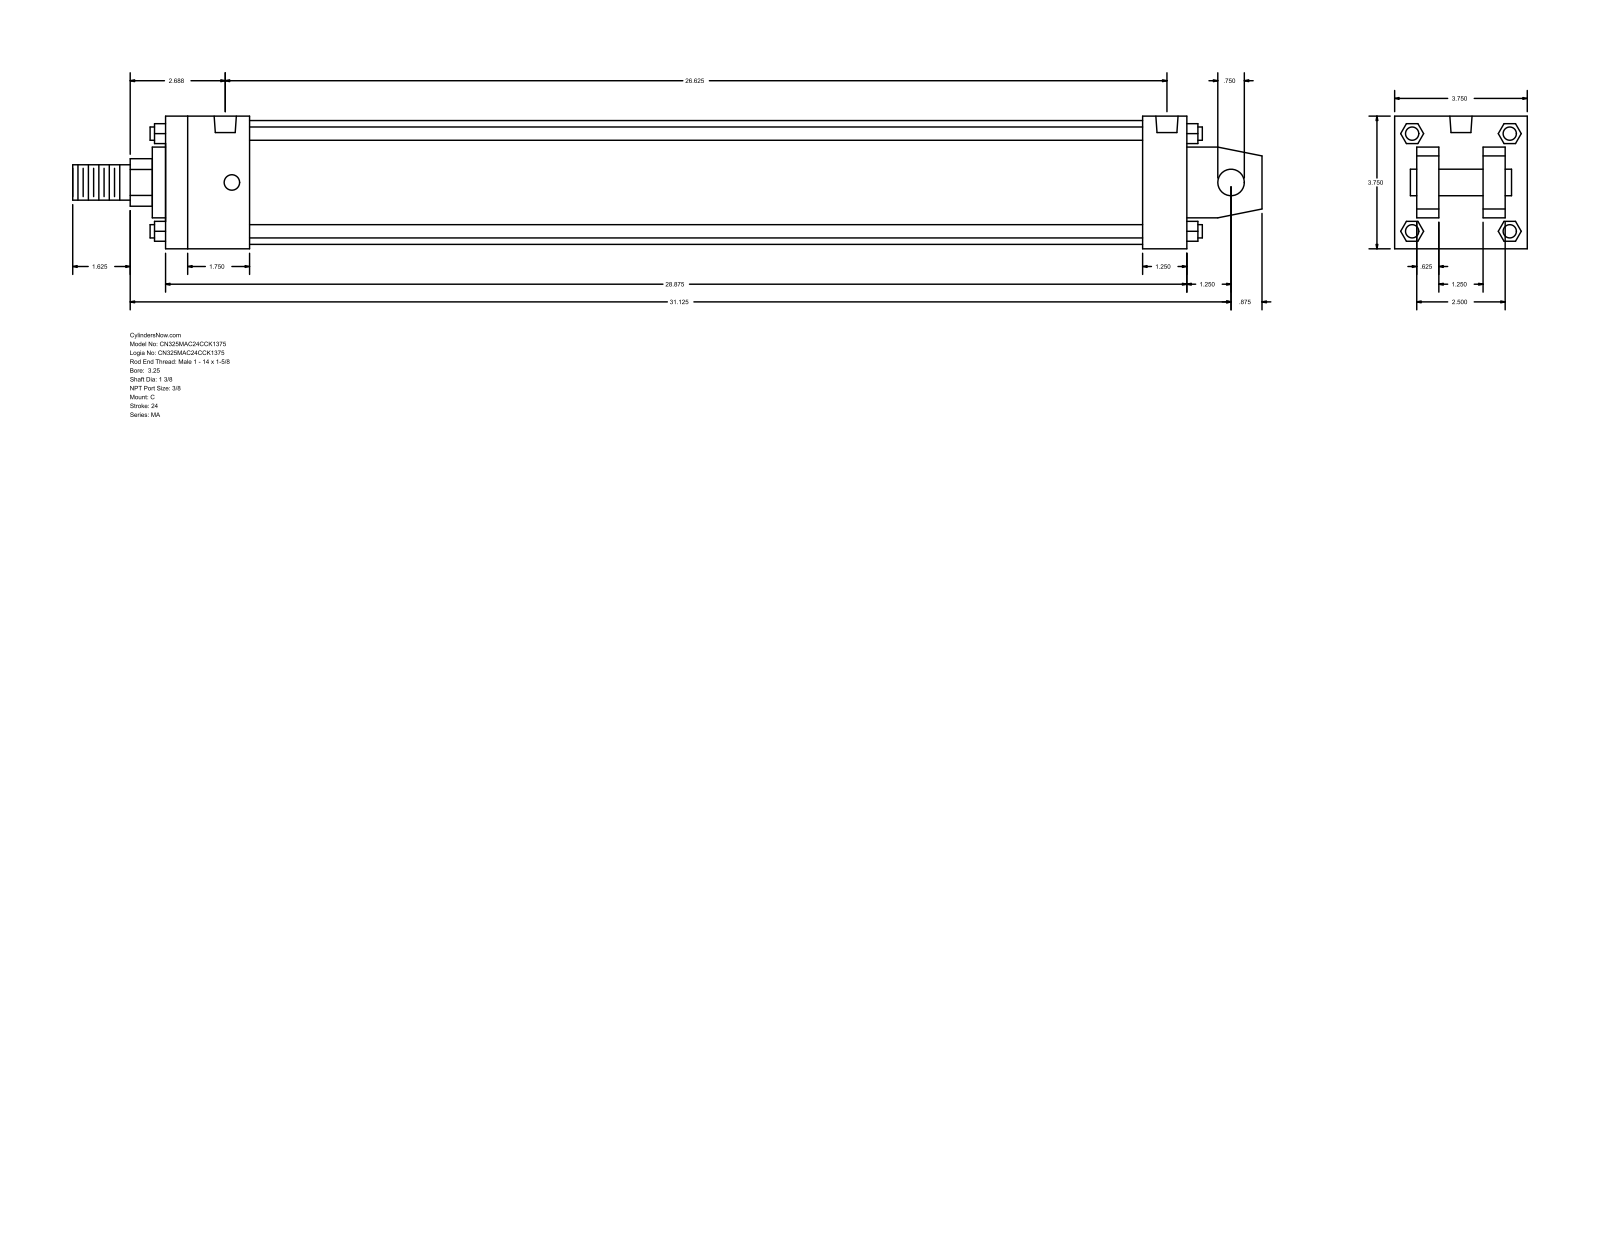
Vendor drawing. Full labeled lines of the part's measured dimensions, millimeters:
Part name (STEP PRODUCT): MA_C__0325_1.375
STEP written by: GSSL Pune (CONFIG_CONTROL_DESIGN)
Units: millimetres
Bodies: 0 solids, 139 faces (108 planar, 31 cylindrical, 0 other)
Overall size (bounding box): 854.08 × 95.25 × 95.25
Round holes (diameter × count): ⌀11.11 ×4, ⌀15.93 ×2
Round bosses / shafts (diameter × count): ⌀9.53 ×4, ⌀88.9 ×1, ⌀50.8 ×1, ⌀34.92 ×1, ⌀25.4 ×1, ⌀19.05 ×1
Partial cylindrical surfaces — rounded edges, fillets, slot ends (radius × count): R17.06 ×1
Main face-to-face distances: 95.24, 15.87, 63.5, 733.43, 31.74, 79.37, 47.63, 701.68, 31.75, 60.32
Hole centre spacings: 4.77, 666.74, 671.51, 676.28
